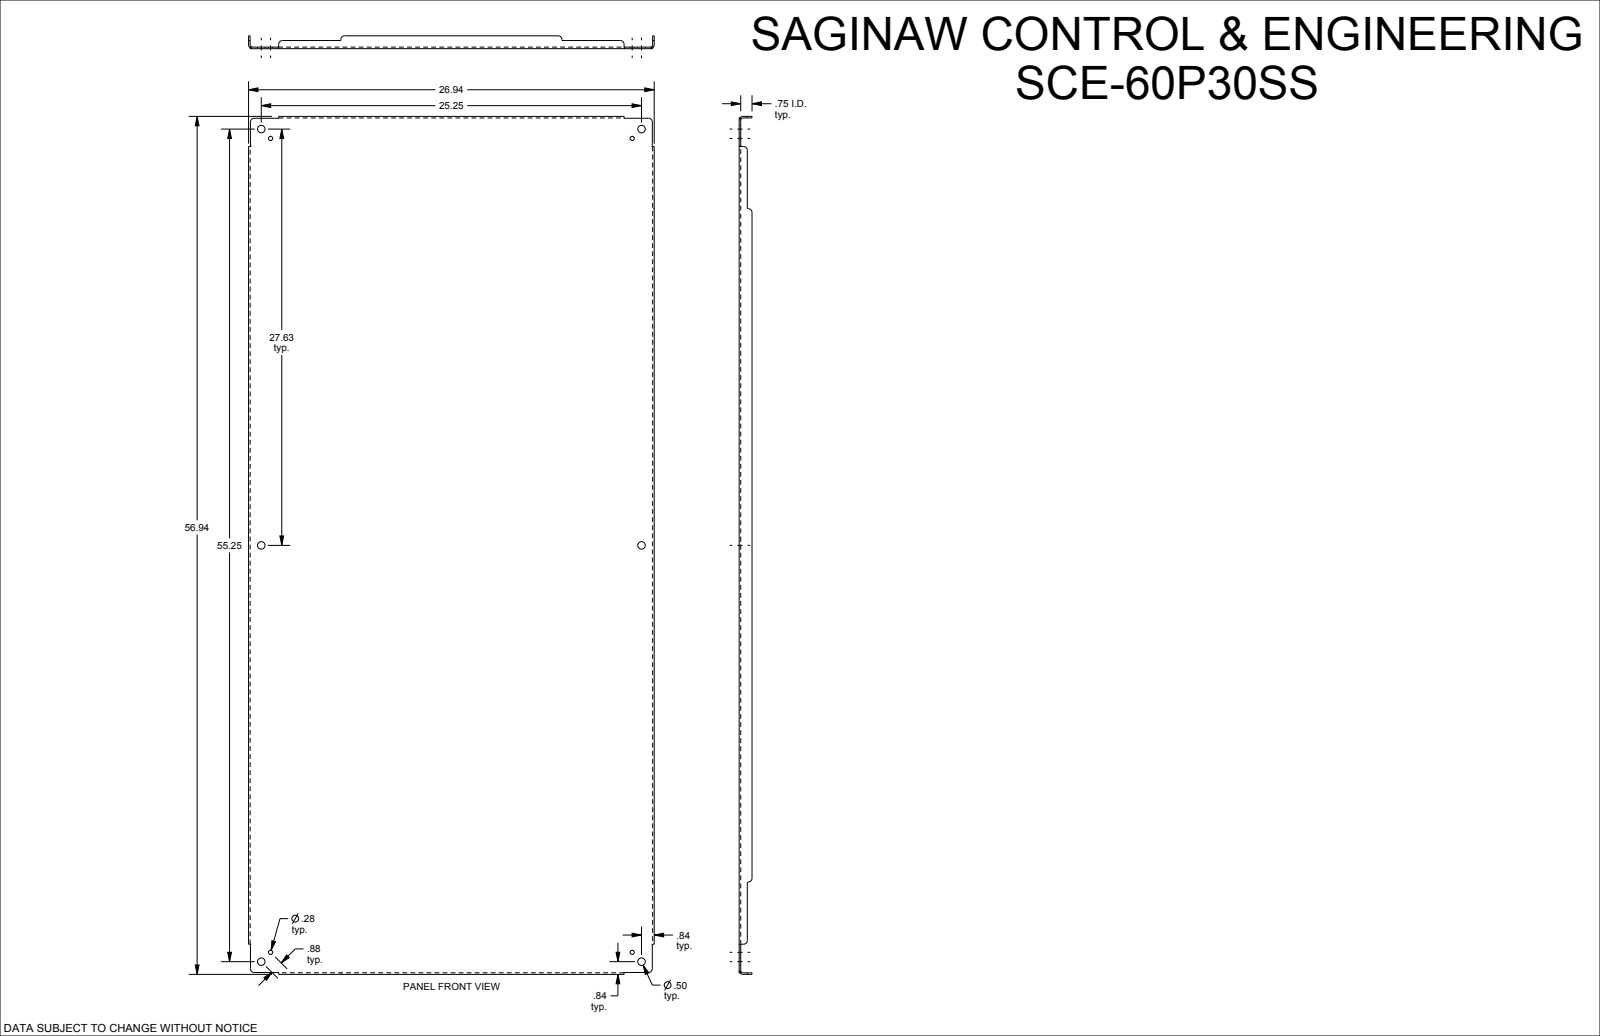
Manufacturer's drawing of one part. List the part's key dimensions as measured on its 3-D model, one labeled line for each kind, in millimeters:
Part name (STEP PRODUCT): SCE-60P30SS
STEP written by: SolidWorks 2019 (CONFIG_CONTROL_DESIGN)
Units: millimetres
Bodies: 1 solid, 108 faces (46 planar, 38 cylindrical, 24 other)
Overall size (bounding box): 1446.2 × 684.2 × 21.7
Volume: 2 763 000 mm³ · Surface area: 2 104 000 mm²
Round holes (diameter × count): ⌀12.7 ×6, ⌀7.1 ×4
Partial cylindrical surfaces — rounded edges, fillets, slot ends (radius × count): R6.4 ×12, R6.2 ×4, R3.6 ×2, R3.6 ×2
Main face-to-face distances: 2.6, 2.6, 681.6, 684.2, 678.9, 1443.6, 19.1, 21.7, 1446.2, 1440.9
Hole centre spacings: 22.2, 625.8, 686.1, 701.7, 928.4, 950.6, 1387.7, 1522.1
